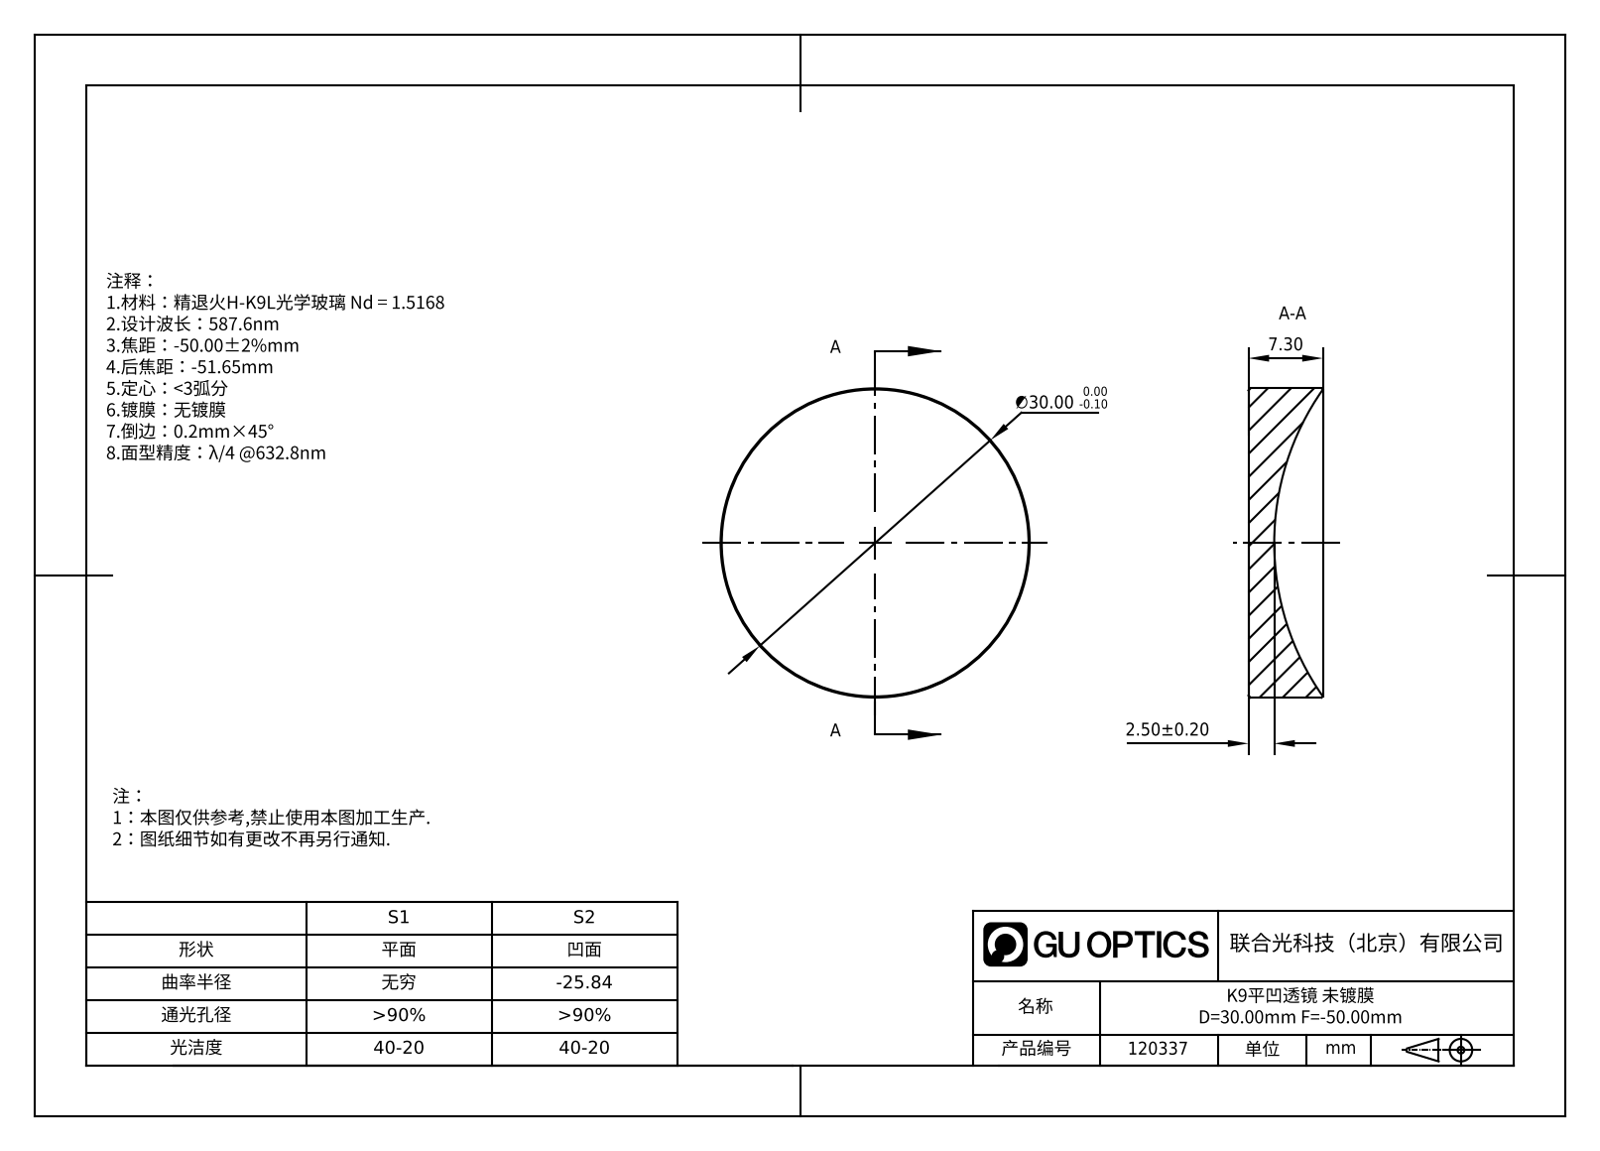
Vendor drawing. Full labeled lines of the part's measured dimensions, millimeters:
Part name (STEP PRODUCT): GL13-030-050
STEP written by: SolidWorks 2022 (AUTOMOTIVE_DESIGN)
Units: millimetres
Bodies: 1 solid, 9 faces (1 planar, 2 cylindrical, 6 other)
Overall size (bounding box): 30 × 30 × 7.22
Volume: 3 403 mm³ · Surface area: 2 146 mm²
Round bosses / shafts (diameter × count): ⌀30 ×1
